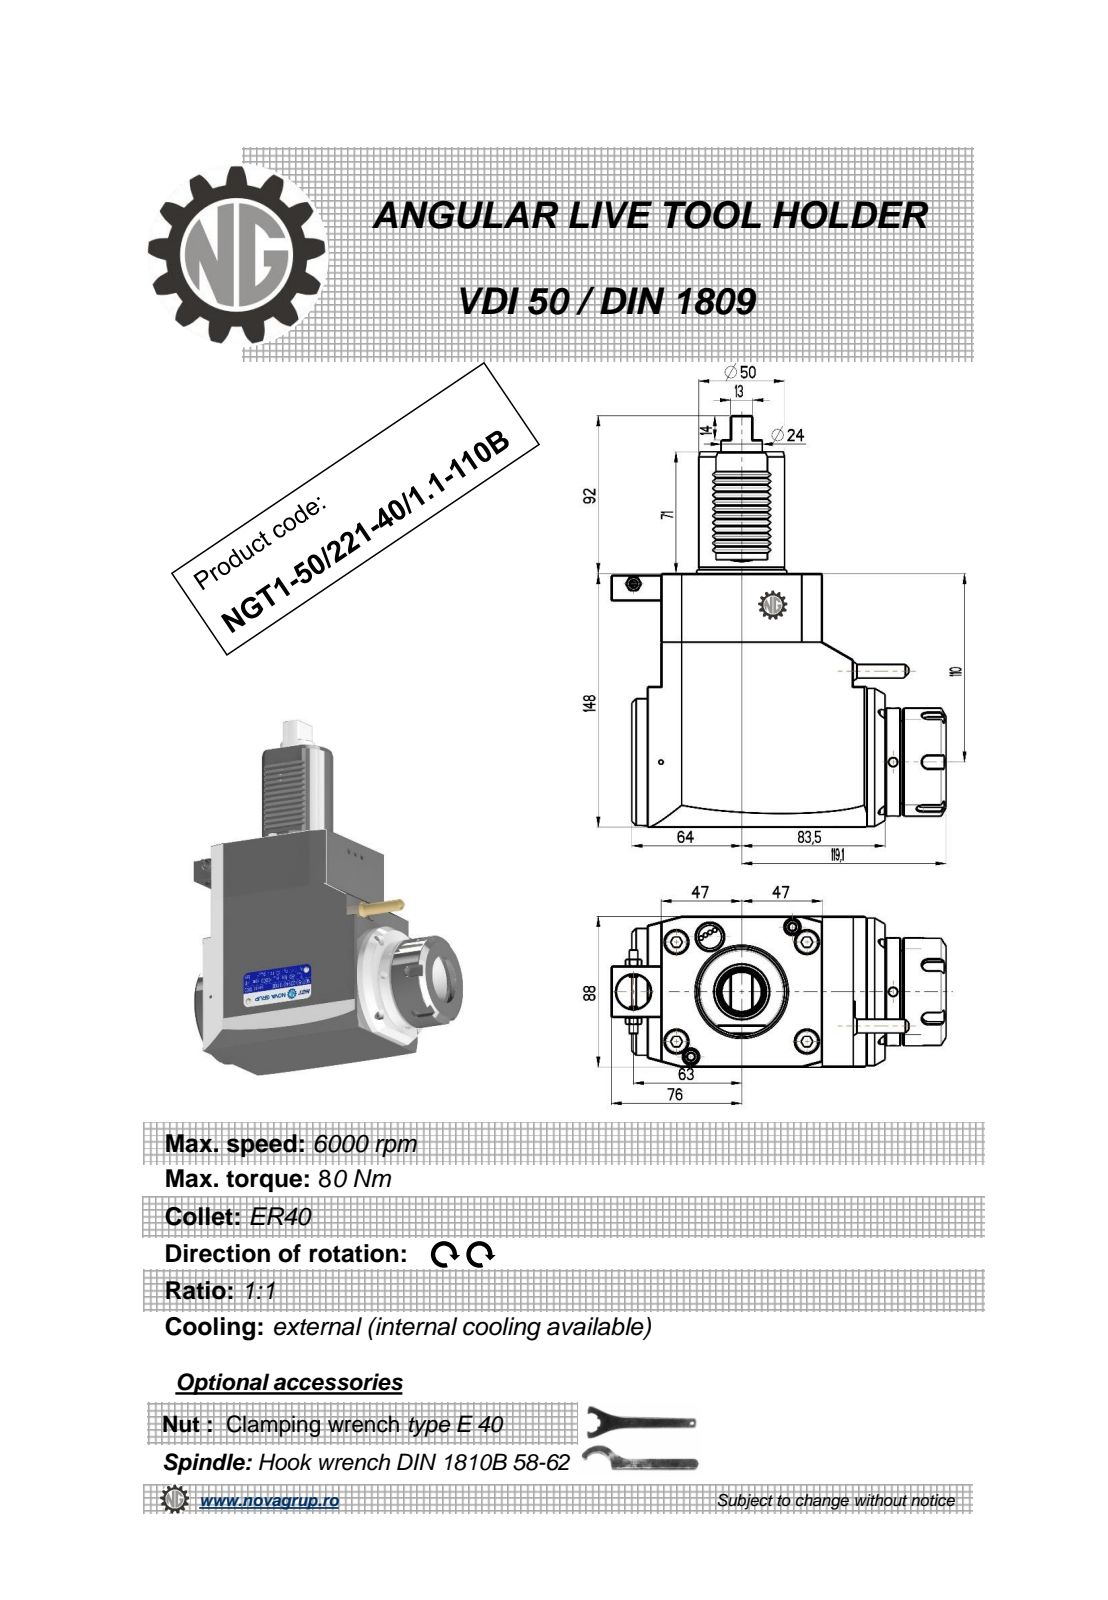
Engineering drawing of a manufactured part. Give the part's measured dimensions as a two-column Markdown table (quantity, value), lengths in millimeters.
| quantity | value |
| --- | --- |
| part name | NGT1_50_221_40_1_1_110B |
| STEP written by | PRO/ENGINEER BY PARAMETRIC TECHNOLOGY CORPORATION, 2010280 (CONFIG_CONTROL_DESIGN) |
| units | millimeters |
| bodies | 1 solid, 431 faces (210 planar, 99 cylindrical, 122 other) |
| overall size | 240 × 195.1 × 88 |
| volume | 1 829 000 mm³ |
| surface area | 114 078 mm² |
| round holes (diameter × count) | 5 × 3, 3.8 × 2, 4 × 2, 3 × 1, 9.5 × 1, 20 × 1, 33.5 × 1 |
| round bosses / shafts (diameter × count) | 86 × 1, 74 × 1, 63 × 1, 51 × 1, 50 × 1, 24 × 1, 10 × 1, 8.96 × 1 |
| partial cylindrical surfaces (radius × count) | 0.26 × 12, 0.3 × 12, 0.2 × 6, 3.75 × 5, 0.8 × 2, 2.5 × 1 |
| main face-to-face distances | 88, 148, 147.5, 17, 8, 94, 111, 9, 130.5, 36.5 |
| hole center spacings | 9, 101.9, 18, 49.73, 52.46, 56.51, 56.65, 101.5 |
